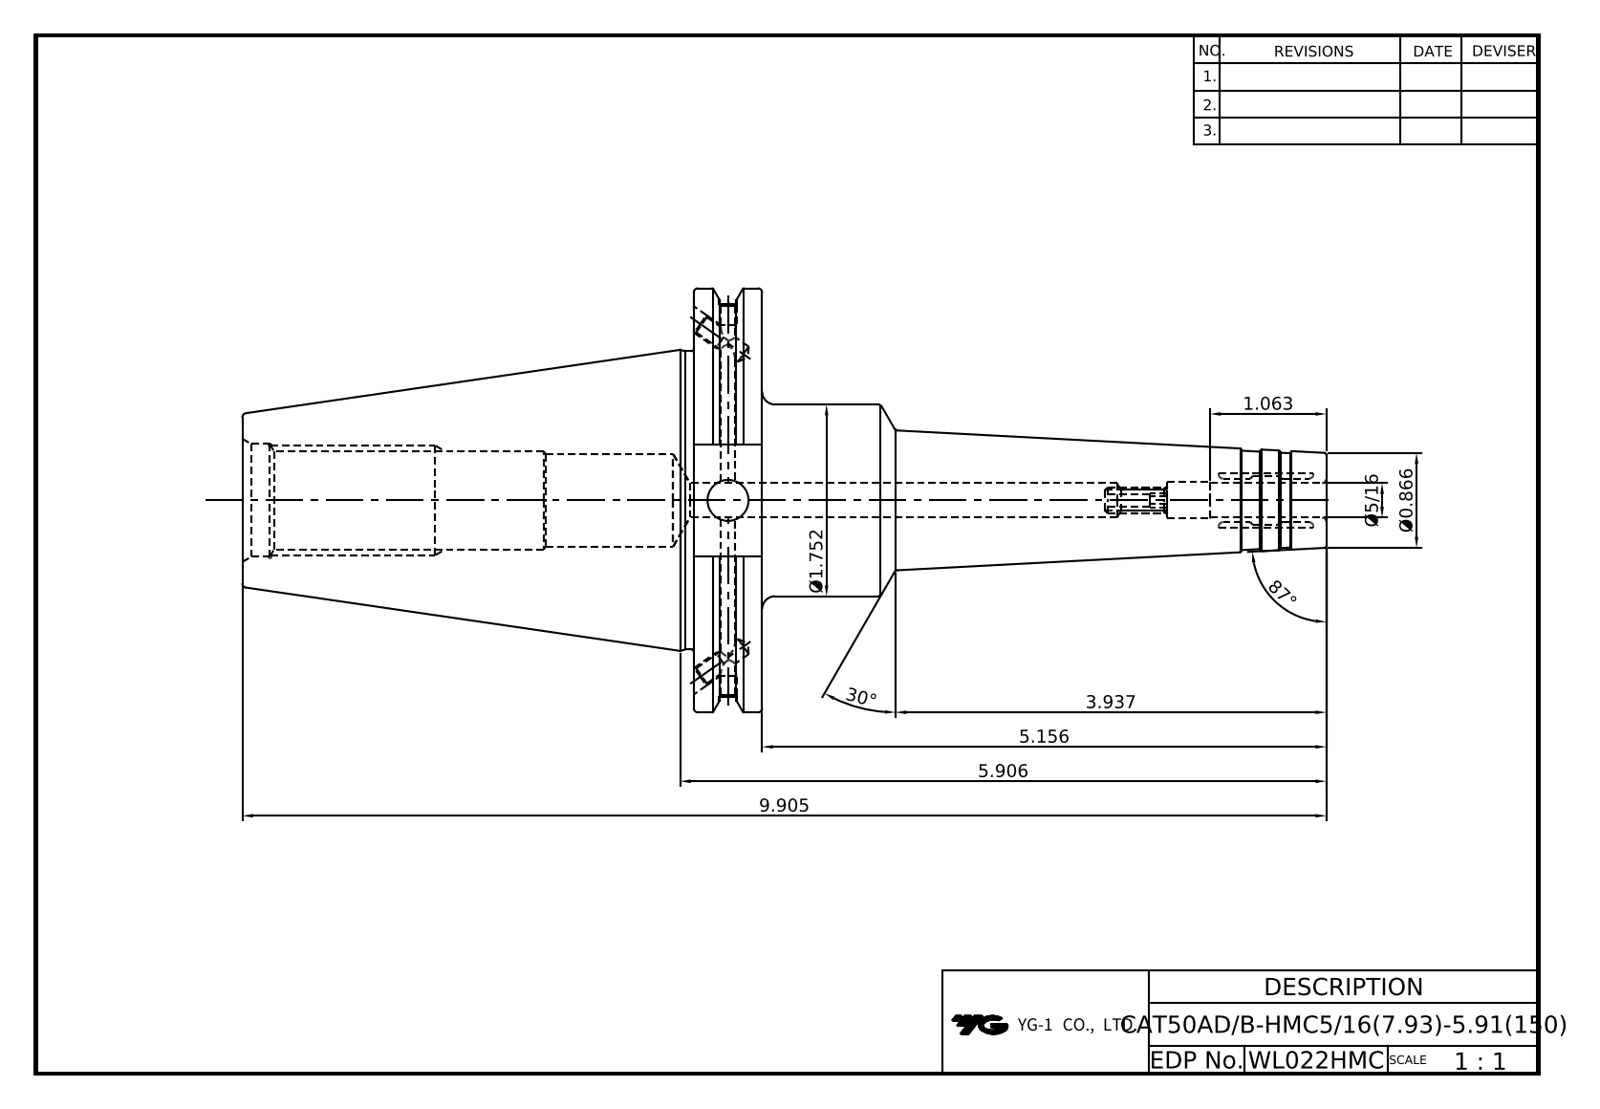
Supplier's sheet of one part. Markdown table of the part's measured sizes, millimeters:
| quantity | value |
| --- | --- |
| part name | LO-CAT50ADB-HMC7.9375-150 |
| STEP written by | Autodesk Inventor 2024 (AUTOMOTIVE_DESIGN) |
| units | millimeters |
| bodies | 1 solid, 106 faces (37 planar, 28 cylindrical, 41 other) |
| overall size | 251.6 × 98.42 × 94.69 |
| volume | 424 025 mm³ |
| surface area | 59 639 mm² |
| round holes (diameter × count) | 3.24 × 2, 4.13 × 2, 4.2 × 2, 5 × 2, 4.92 × 1, 7.94 × 1, 8 × 1, 9.5 × 1, 9.53 × 1, 21.5 × 1, 21.97 × 1, 26.2 × 1 |
| round bosses / shafts (diameter × count) | 98.42 × 1, 91.29 × 1, 69.25 × 1, 44.5 × 1 |
| main face-to-face distances | 15.88, 104.77, 120.65, 73.03, 251.6, 146.83, 130.95, 25.9, 110.82, 6.05 |
